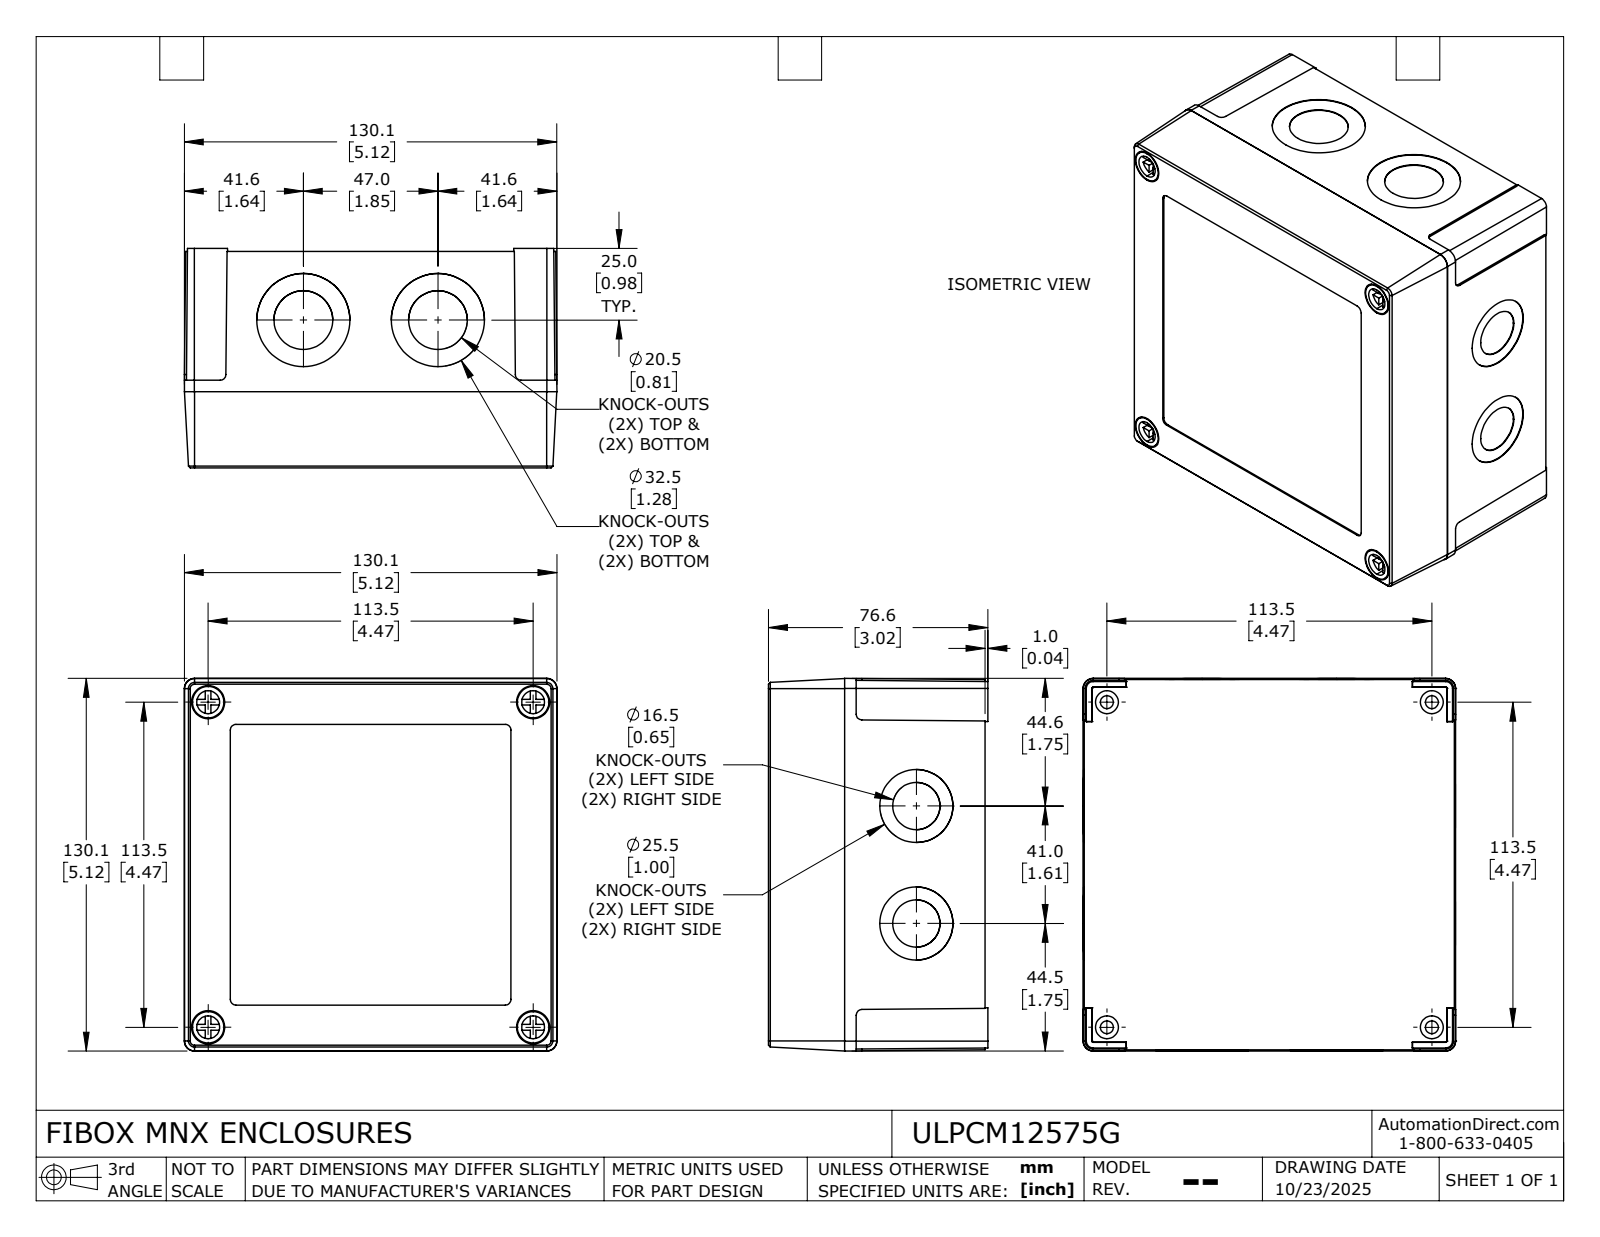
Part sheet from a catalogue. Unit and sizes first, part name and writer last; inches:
Units: inches
Overall size (bounding box): 5.122 × 5.122 × 3.016
Round holes (diameter × count): ⌀0.126 ×8, ⌀0.157 ×8, ⌀0.177 ×4, ⌀0.315 ×4, ⌀0.457 ×4, ⌀0.65 ×4, ⌀0.807 ×4, ⌀1.004 ×4, ⌀1.28 ×4
Round bosses / shafts (diameter × count): ⌀0.315 ×8, ⌀0.098 ×8, ⌀0.433 ×4, ⌀0.283 ×4
Partial cylindrical surfaces — rounded edges, fillets, slot ends (radius × count): R0.079 ×8, R0.056 ×6, R0.021 ×4, R0.197 ×4, R0.023 ×2
Main face-to-face distances: 0.165, 2.878, 0.118, 2.76, 0.079, 2.839, 2.957, 2.858, 0.098, 0.02
Hole centre spacings: 2.281, 4.587, 0.888, 1.476, 1.796, 2.506, 3.543, 3.7
Volume: 15.37 in³ · Surface area: 239.4 in²
Bodies: 6 solids, 522 faces (298 planar, 184 cylindrical, 40 other)
Part name (STEP PRODUCT): ULPCM12575G_Default
STEP written by: SolidWorks 2024 (CONFIG_CONTROL_DESIGN)
